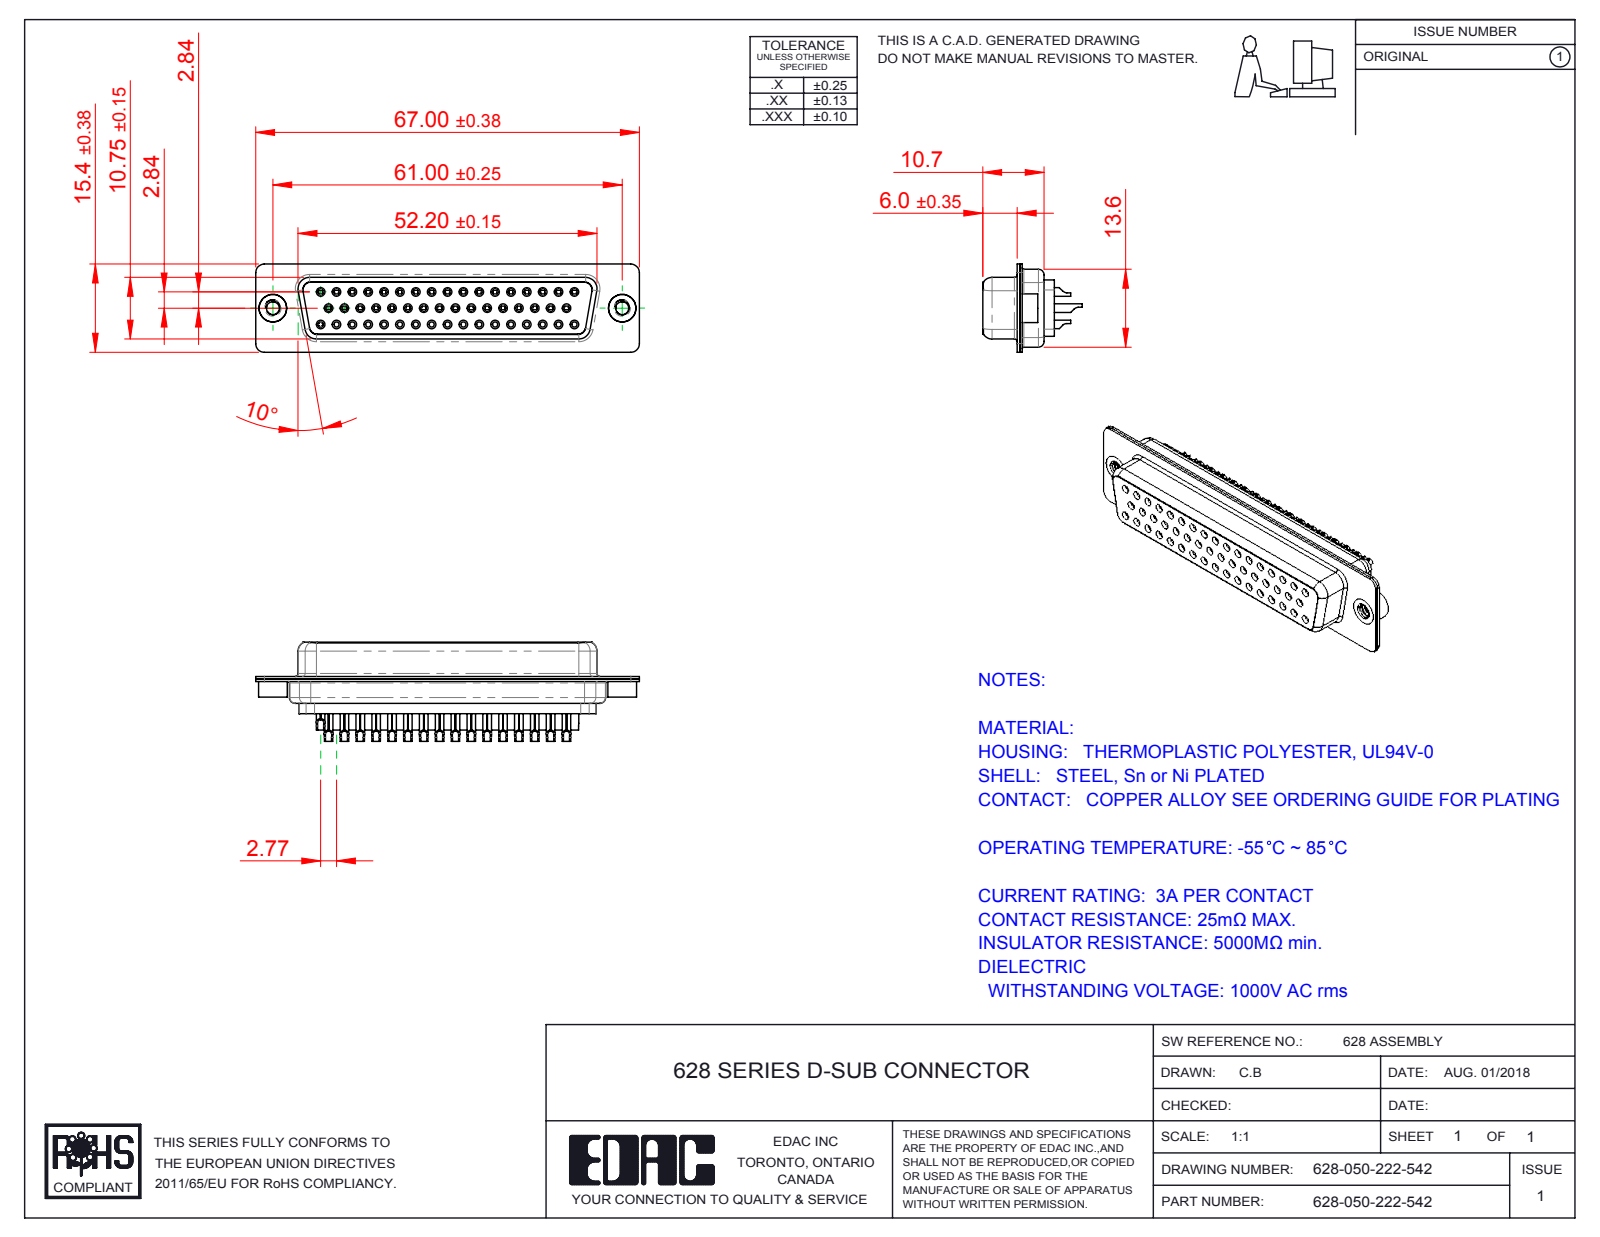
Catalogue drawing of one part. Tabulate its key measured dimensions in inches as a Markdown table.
| quantity | value |
| --- | --- |
| part name | 628 Contact Row 2_22M; 628 Contact Row 1_22L; 628 Shell Rear_50 Contacts; 628 Housing_50 LP (+4 more) |
| STEP written by | SolidWorks 2016 (CONFIG_CONTROL_DESIGN) |
| units | inches |
| bodies | 39 solids, 3513 faces (829 planar, 1115 cylindrical, 1569 other) |
| overall size | 2.638 × 0.683 × 0.606 |
| volume | 0.405 in³ |
| surface area | 21.9 in² |
| round holes (diameter × count) | 0.035 × 50, 0.063 × 50, 0.031 × 34, 0.043 × 34, 0.067 × 17, 0.059 × 16, 0.079 × 16, 0.089 × 2, 0.157 × 2, 0.189 × 2 |
| round bosses / shafts (diameter × count) | 0.079 × 34, 0.059 × 34, 0.047 × 34, 0.197 × 2, 0.193 × 2 |
| partial cylindrical surfaces (radius × count) | 0.011 × 33, 0.059 × 16, 0.079 × 12, 0.053 × 8, 0.039 × 7, 0.01 × 4, 0.02 × 4, 0.024 × 4 |
| main face-to-face distances | 0.018, 0.016, 0.406, 0.035, 0.238, 0.256, 0.492, 0.254, 0.236, 0.446 |
| hole center spacings | 0.124, 0.109, 0.218, 0.327, 0.436, 0.545, 0.654, 0.763 |
